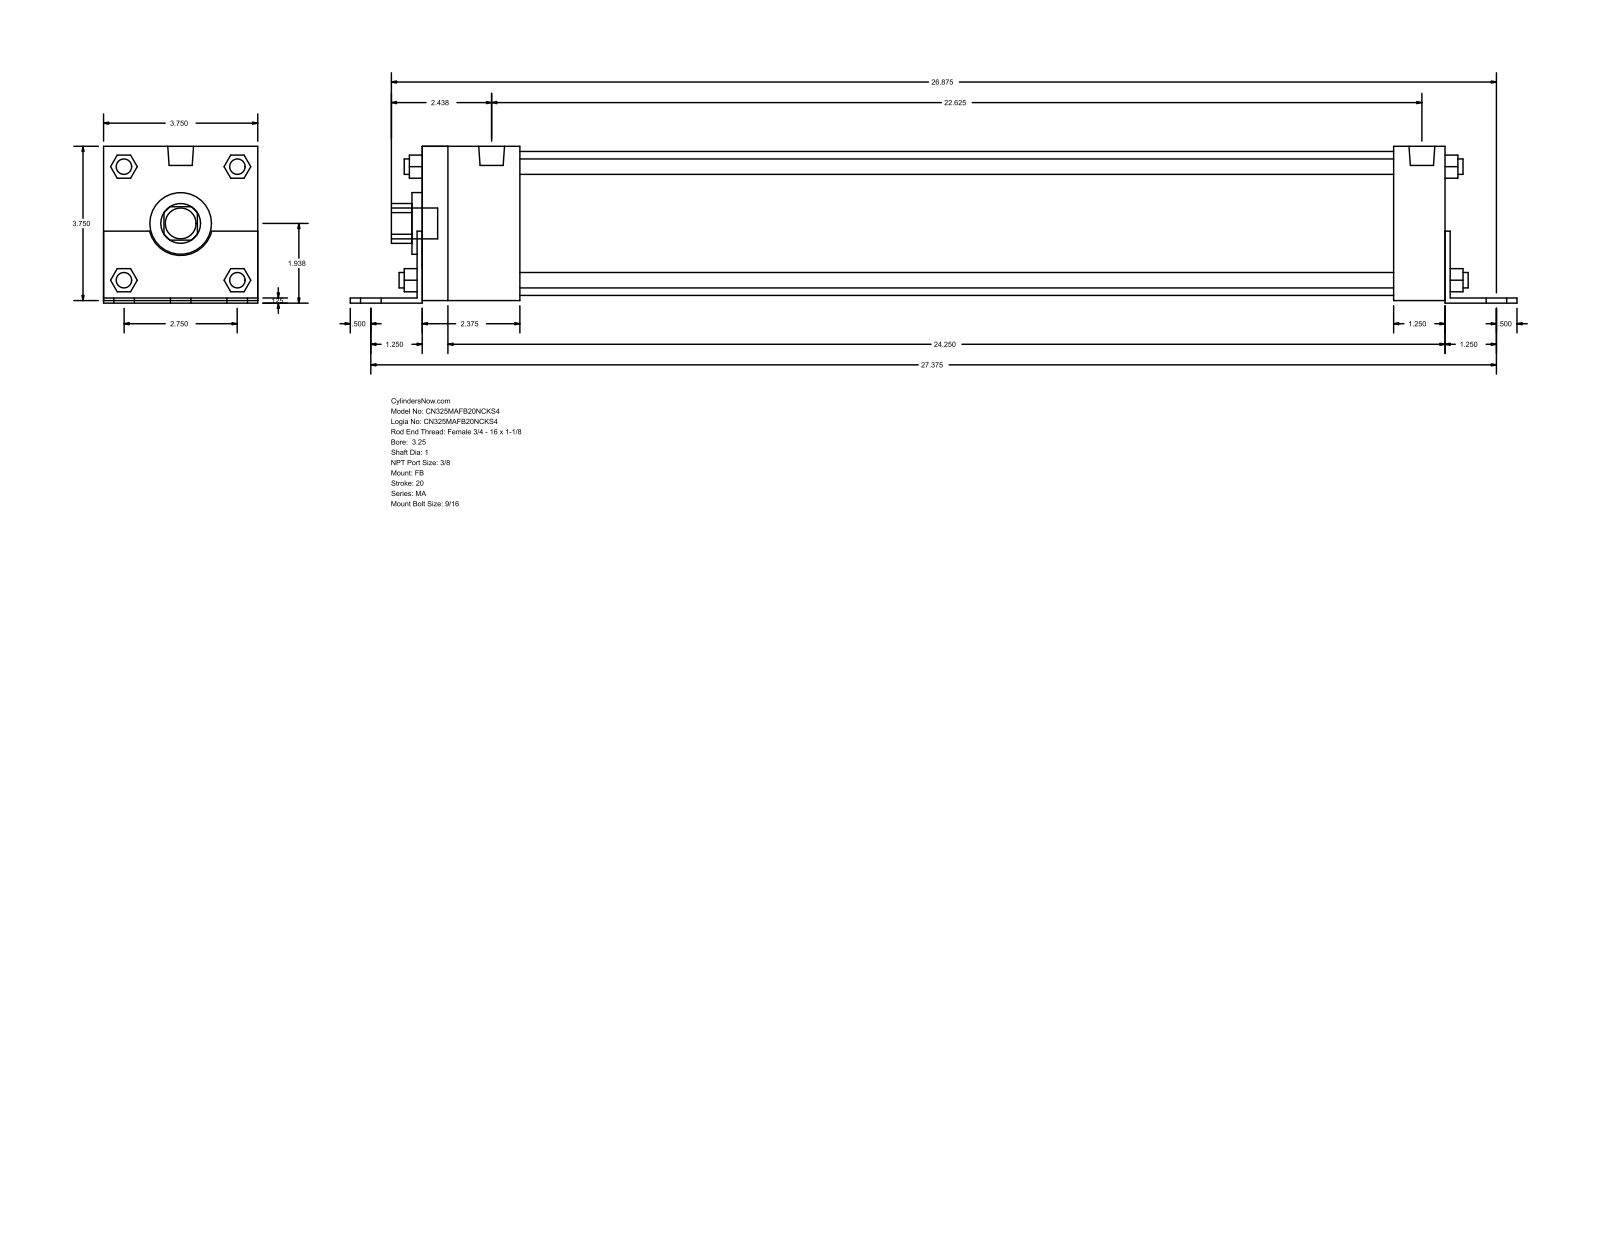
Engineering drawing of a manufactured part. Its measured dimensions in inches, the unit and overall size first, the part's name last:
Units: inches
Overall size (bounding box): 28.375 × 3.813 × 3.75
Round holes (diameter × count): ⌀1 ×1, ⌀1.5 ×1, ⌀3.5 ×1
Round bosses / shafts (diameter × count): ⌀0.563 ×6, ⌀0.437 ×4, ⌀0.375 ×4, ⌀0.627 ×2, ⌀0.75 ×1
Partial cylindrical surfaces — rounded edges, fillets, slot ends (radius × count): R0.484 ×1, R0.78 ×1
Main face-to-face distances: 3.75, 0.125, 0.063, 3.812, 0.062, 3.687, 25, 24.875, 25.125, 1.375
Bodies: 0 solids, 140 faces (105 planar, 35 cylindrical, 0 other)
Part name (STEP PRODUCT): MA_FB__0325_1
STEP written by: GSSL Pune (CONFIG_CONTROL_DESIGN)
